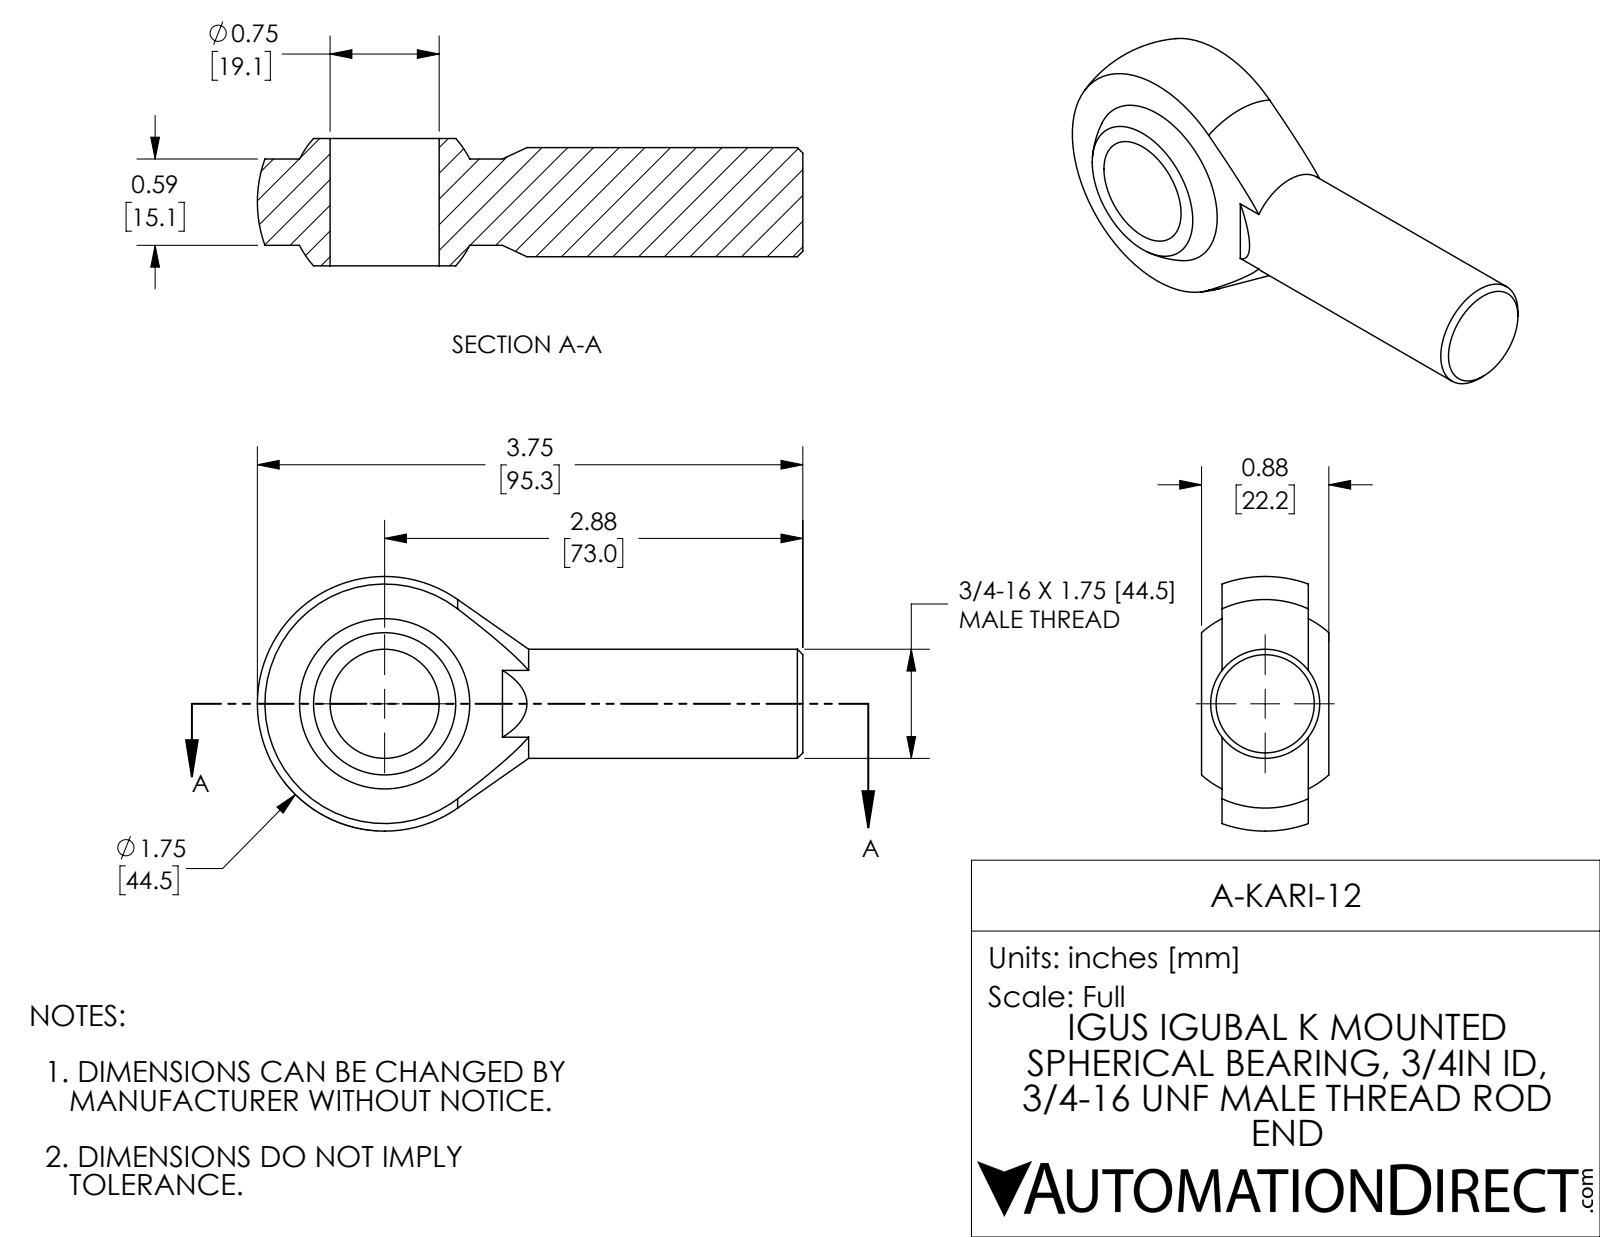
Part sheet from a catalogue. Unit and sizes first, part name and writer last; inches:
Units: inches
Overall size (bounding box): 3.715 × 1.75 × 0.875
Round holes (diameter × count): ⌀0.75 ×1
Round bosses / shafts (diameter × count): ⌀0.75 ×1
Main face-to-face distances: 0.593, 0.141, 0.734, 0.875
Volume: 2.175 in³ · Surface area: 14.13 in²
Bodies: 1 solid, 23 faces (7 planar, 4 cylindrical, 12 other)
Part name (STEP PRODUCT): A-KARI-12
STEP written by: SolidWorks 2017 (AUTOMOTIVE_DESIGN)
